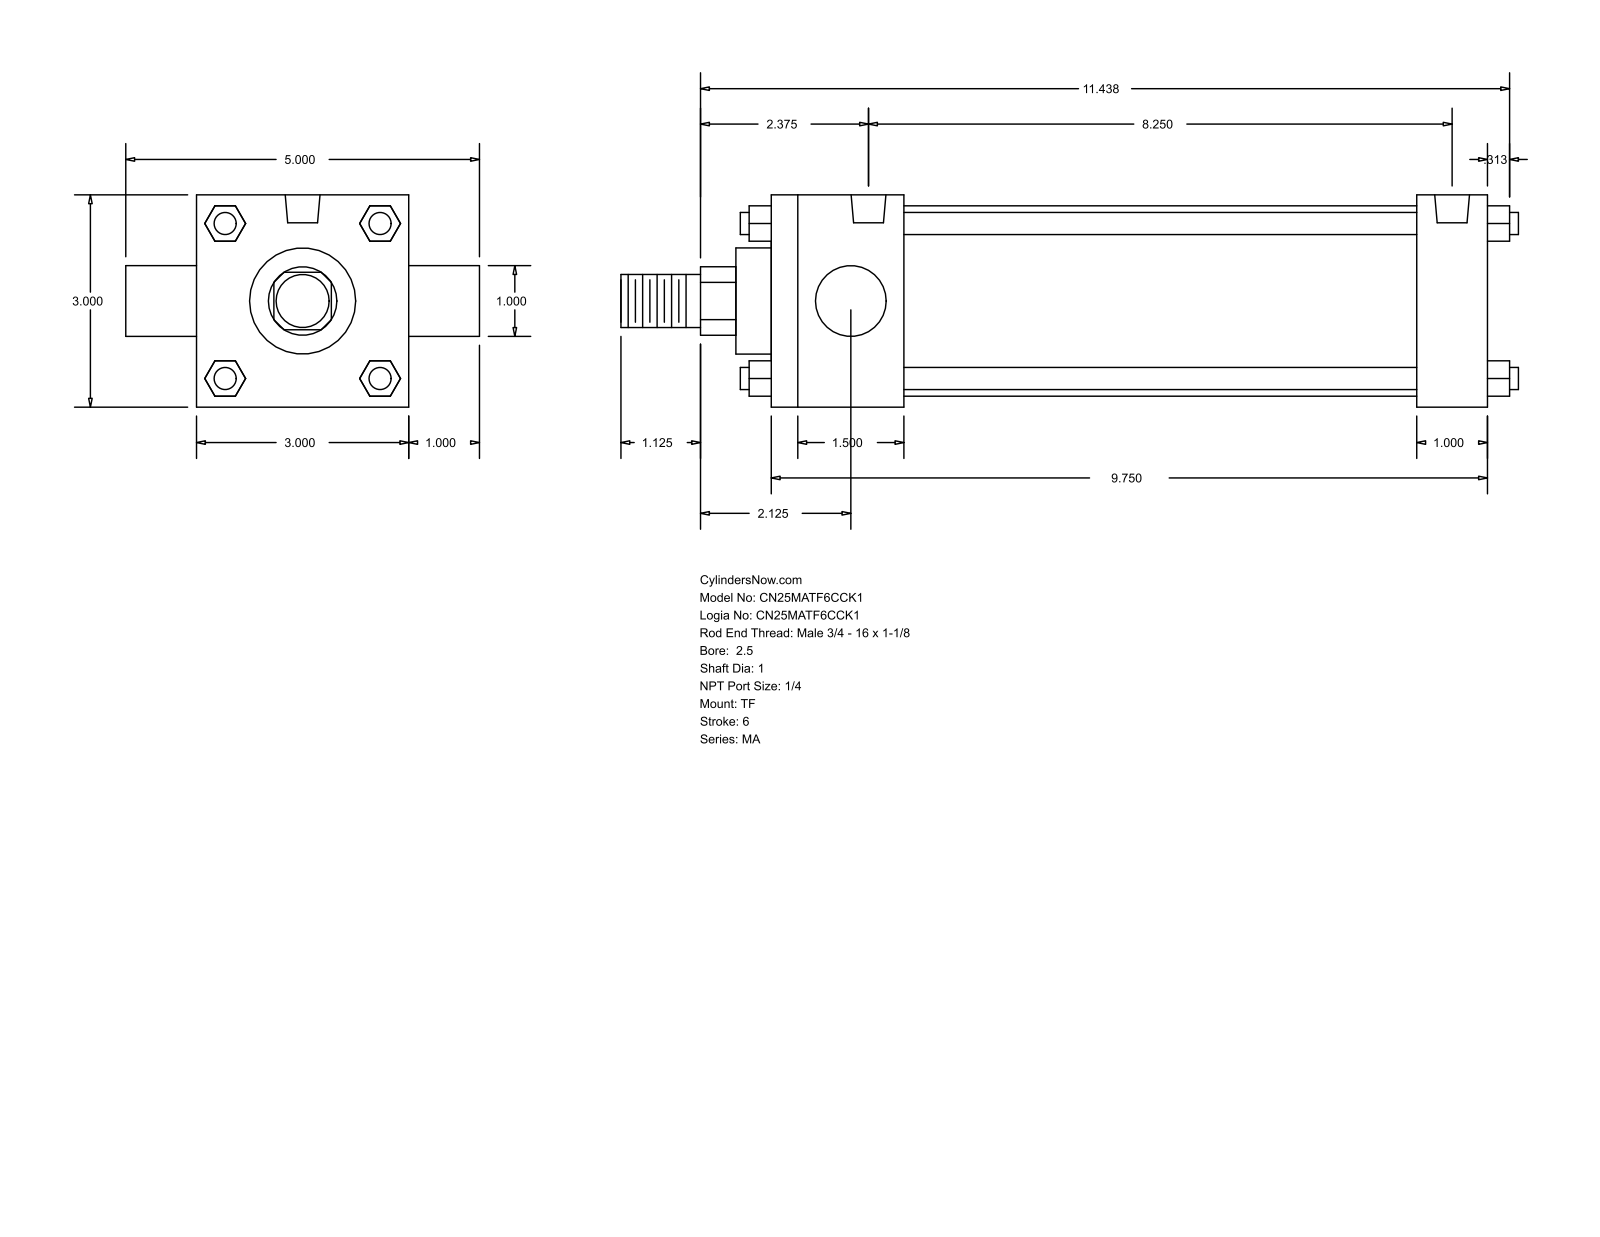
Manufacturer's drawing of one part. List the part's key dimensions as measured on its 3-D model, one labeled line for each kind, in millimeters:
Part name (STEP PRODUCT): MA_TF__0250_1
STEP written by: GSSL Pune (CONFIG_CONTROL_DESIGN)
Units: millimetres
Bodies: 0 solids, 120 faces (92 planar, 28 cylindrical, 0 other)
Overall size (bounding box): 322.26 × 127 × 76.2
Round holes (diameter × count): ⌀7.94 ×3, ⌀12.49 ×2
Round bosses / shafts (diameter × count): ⌀7.94 ×4, ⌀25.4 ×2, ⌀68.33 ×1, ⌀38.1 ×1, ⌀19.05 ×1
Partial cylindrical surfaces — rounded edges, fillets, slot ends (radius × count): R12.29 ×1
Main face-to-face distances: 76.2, 257.17, 12.7, 47.63, 231.78, 184.15, 209.54, 25.39, 101.6, 25.4
Hole centre spacings: 209.55
